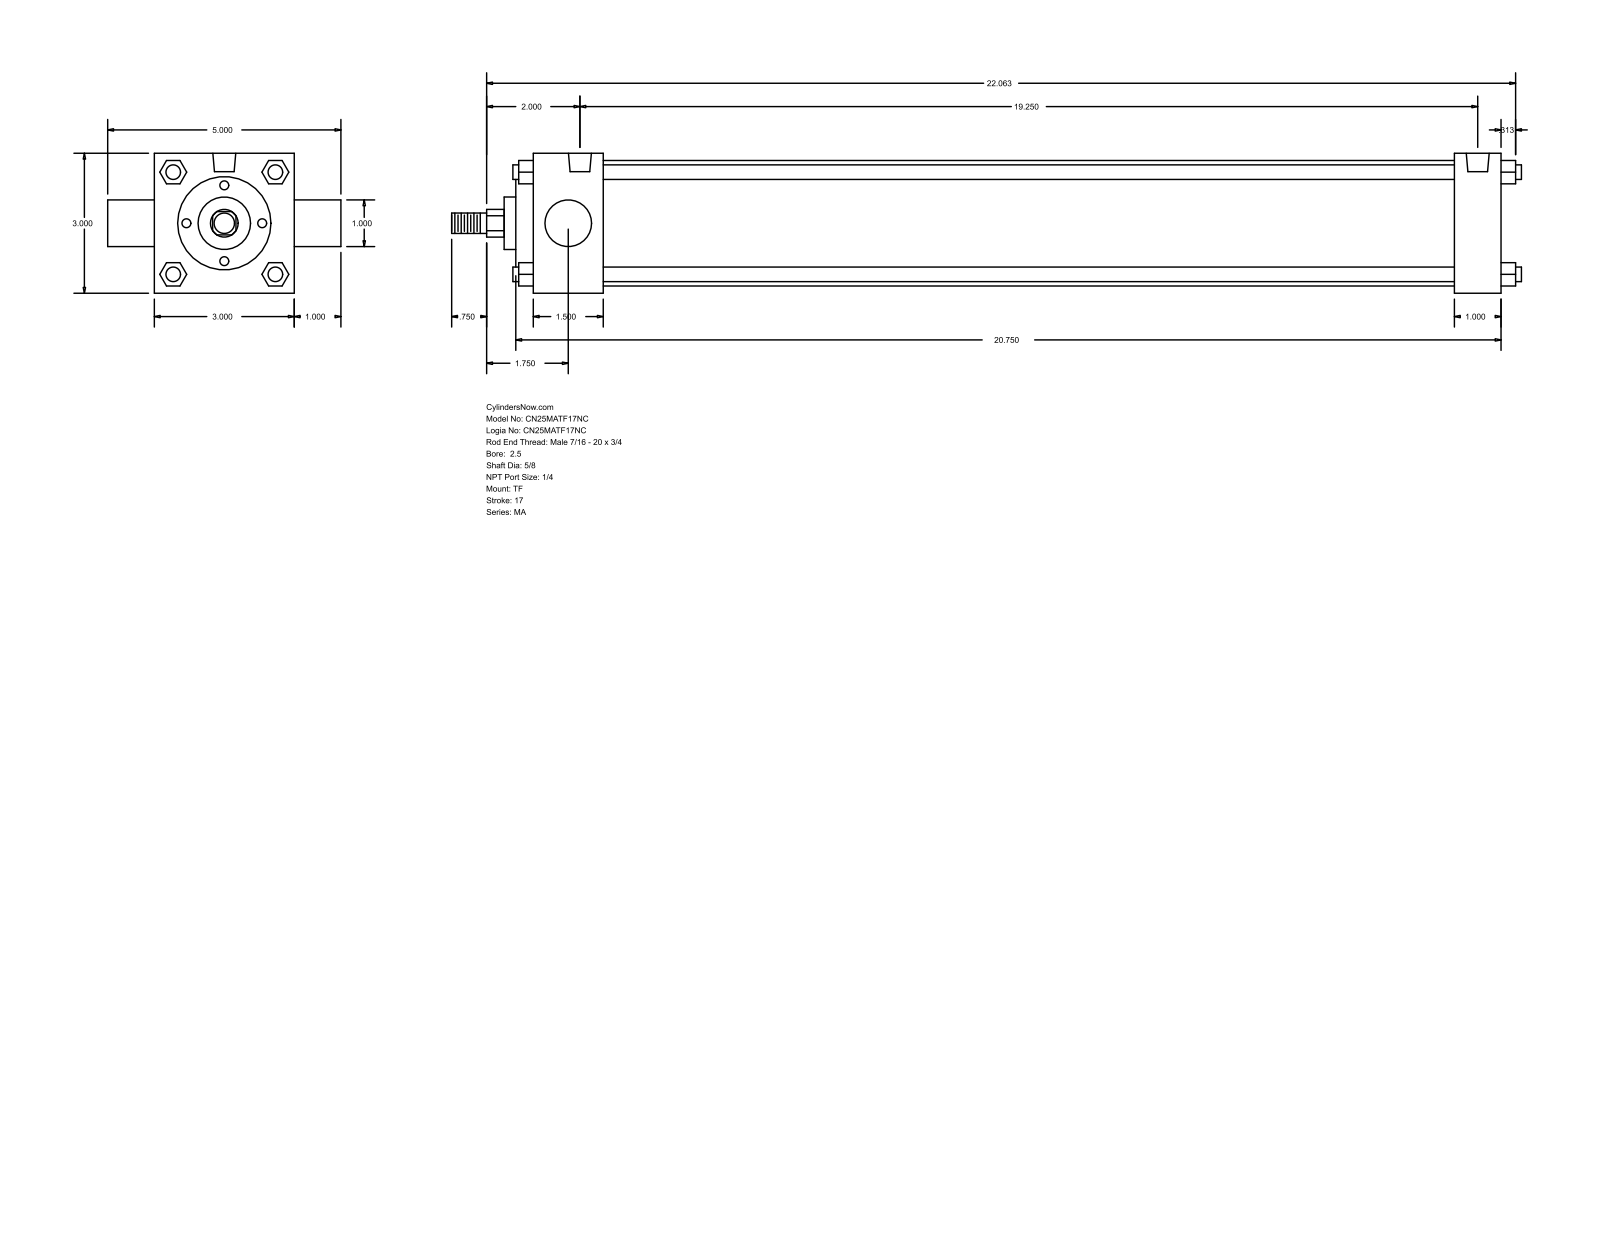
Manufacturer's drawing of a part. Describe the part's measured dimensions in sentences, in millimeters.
The part is named "MA_TF__0250_0.625". Its 3-D file was written by "GSSL Pune (CONFIG_CONTROL_DESIGN)". It is 0 solids with 122 faces: 93 planar, 29 cylindrical and 0 other. Overall it measures 582.61 by 127 by 76.2 millimeters. Round holes: 3 of diameter 7.94, 2 of diameter 12.49. Round bosses or shafts: 4 of diameter 7.94, 1 of diameter 68.33, 1 of diameter 50.8, 1 of diameter 28.57, 1 of diameter 25.4, 1 of diameter 15.88, 1 of diameter 11.11. Partial cylindrical surfaces (rounded edges, fillets, slot ends): 1 of radius 7.54. The main face-to-face distances are 76.2, 527.05, 25.4, 38.1, 501.65, 463.55, 488.95, 12.7, 9.52, 47.62. The hole center spacings are 488.95.
